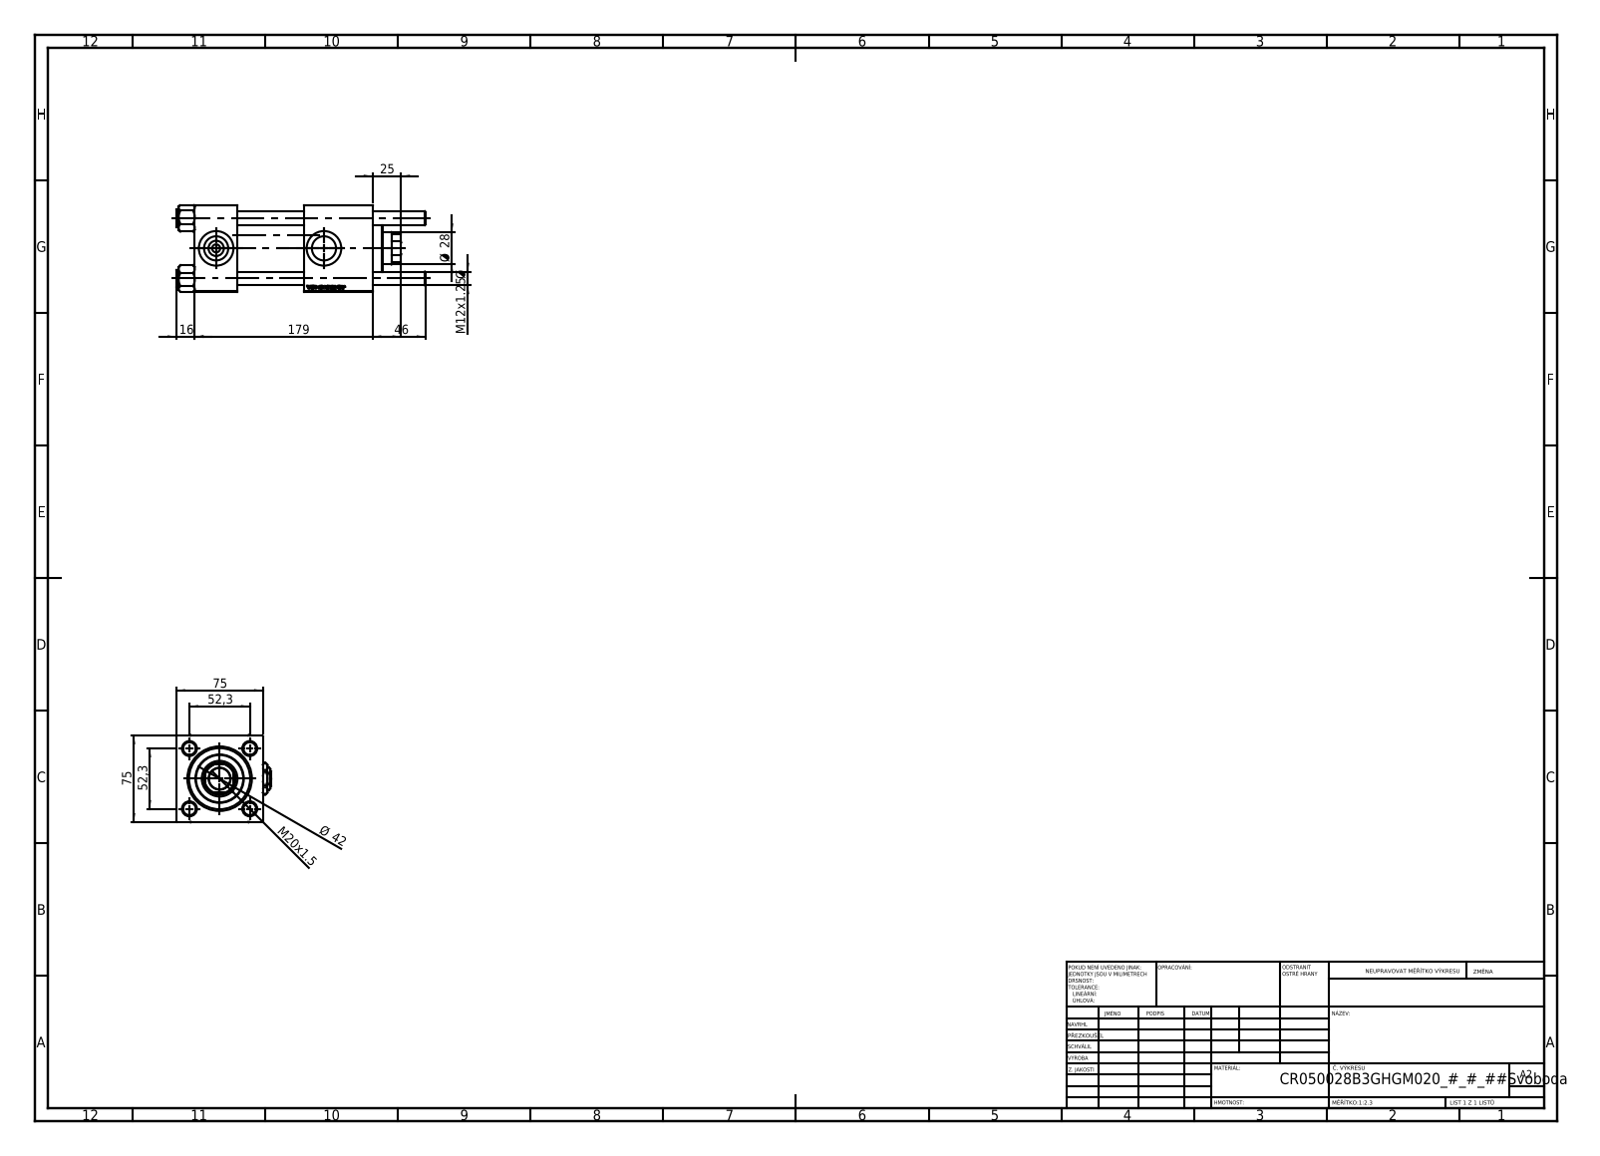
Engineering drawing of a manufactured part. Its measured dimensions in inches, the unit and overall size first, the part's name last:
Units: inches
Overall size (bounding box): 8.504 × 3.228 × 2.97
Round holes (diameter × count): ⌀0.472 ×4, ⌀0.276 ×2, ⌀0.825 ×2, ⌀1.181 ×2, ⌀0.728 ×1, ⌀1.102 ×1, ⌀1.22 ×1, ⌀1.614 ×1, ⌀1.969 ×1, ⌀2.087 ×1
Round bosses / shafts (diameter × count): ⌀0.591 ×4, ⌀2.205 ×1, ⌀1.654 ×1
Partial cylindrical surfaces — rounded edges, fillets, slot ends (radius × count): R0.531 ×1
Main face-to-face distances: 2.953, 1.457, 6.063, 4.606, 3.74, 2.283, 2.323, 4.933, 3.476, 1.193
Hole centre spacings: 1.456, 2.059, 2.912, 3.681
Volume: 42.54 in³ · Surface area: 266 in²
Bodies: 13 solids, 1257 faces (479 planar, 88 cylindrical, 690 other)
Part name (STEP PRODUCT): V215CR_VCP_B; V215CR_B_TYCINKA; V215CR_B-1; Zatka_pro_OIL_PORT (+2 more)
STEP written by: SolidWorks 2019 (CONFIG_CONTROL_DESIGN)
